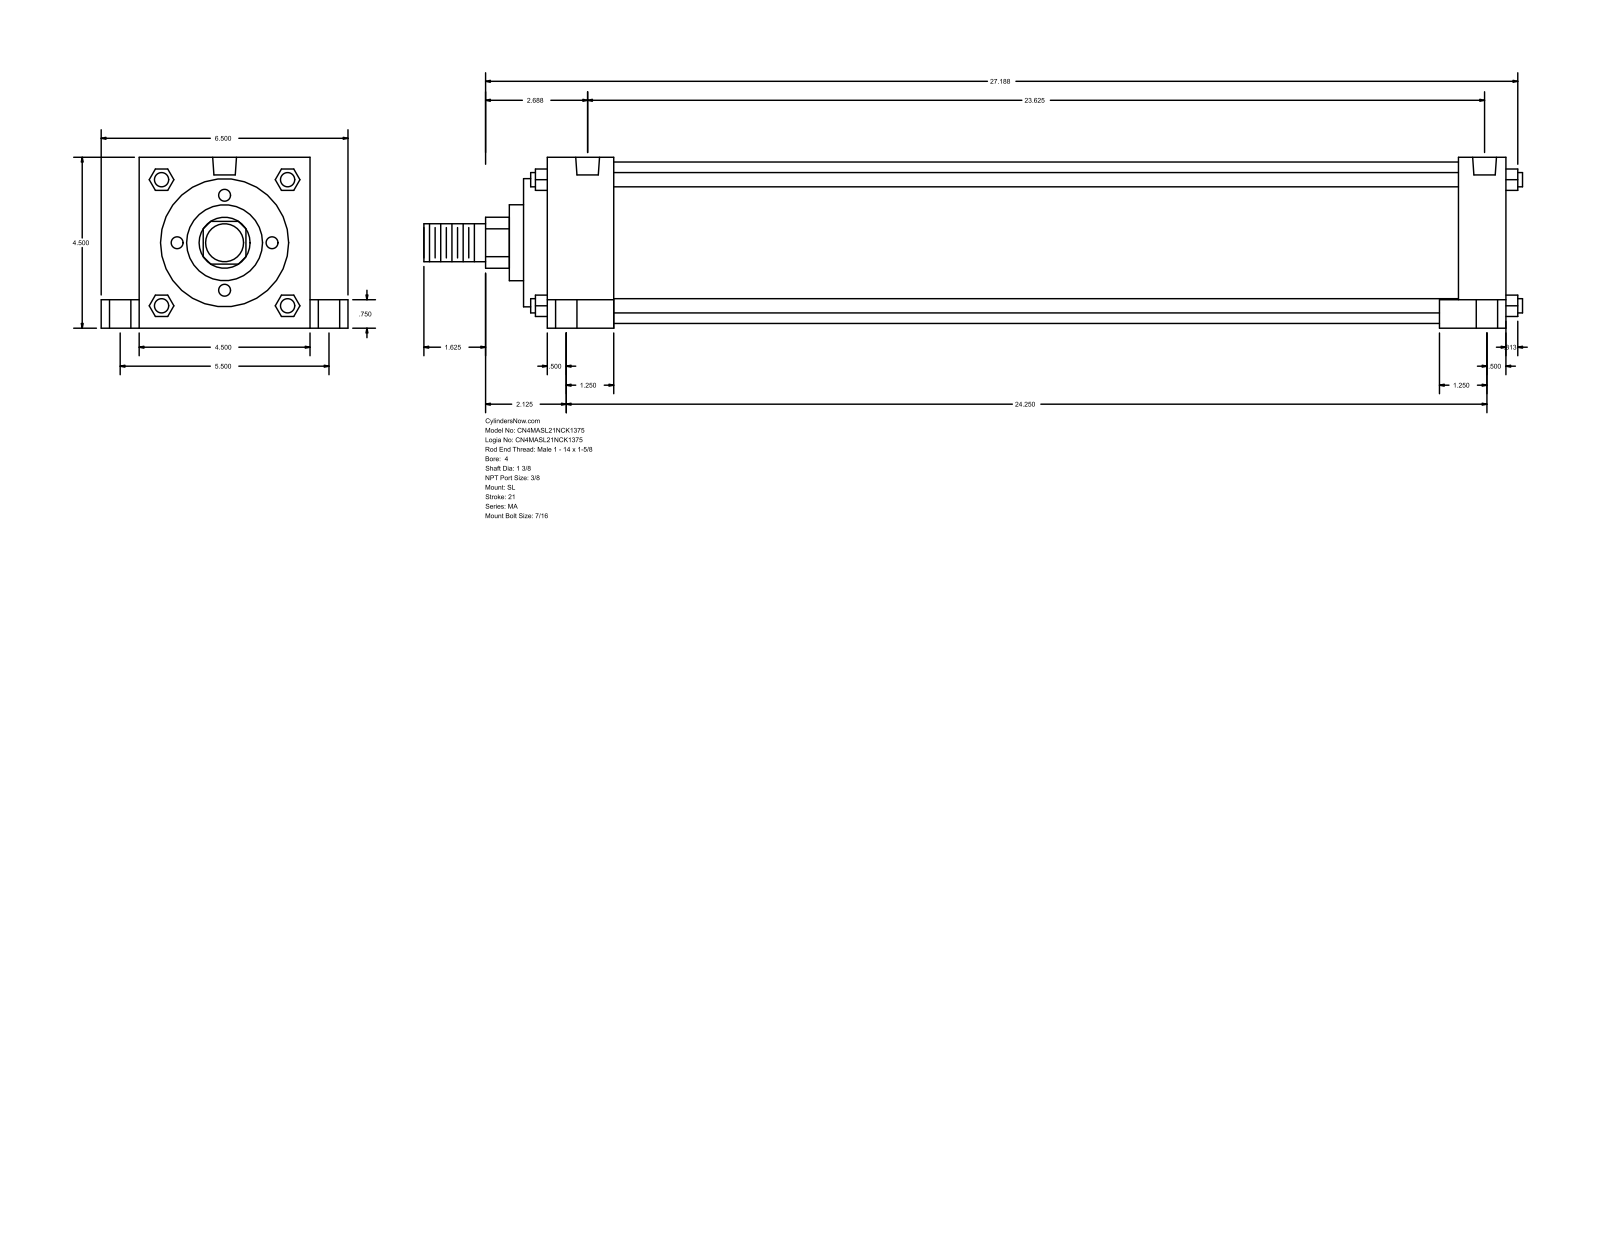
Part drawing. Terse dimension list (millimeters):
name: MA_SL__0400_1.375
written by: GSSL Pune (CONFIG_CONTROL_DESIGN)
unit: mm
bodies: 0 solids, 150 faces (113 planar, 37 cylindrical, 0 other)
size: 735.01 × 165.1 × 114.3
holes: 4× ⌀11.11, 4× ⌀14.29, 4× ⌀20.64, 2× ⌀15.93
bosses: 4× ⌀9.53, 1× ⌀107.95, 1× ⌀85.72, 1× ⌀50.8, 1× ⌀34.92, 1× ⌀25.4
rounds: 1× R17.06
face distances: 114.3, 641.35, 657.22, 15.87, 60.32, 44.45, 596.9, 625.48, 609.61, 565.16
hole spacings: 69.87, 70.14, 71.29, 72.4, 139.7, 590.55, 600.96, 605.7
